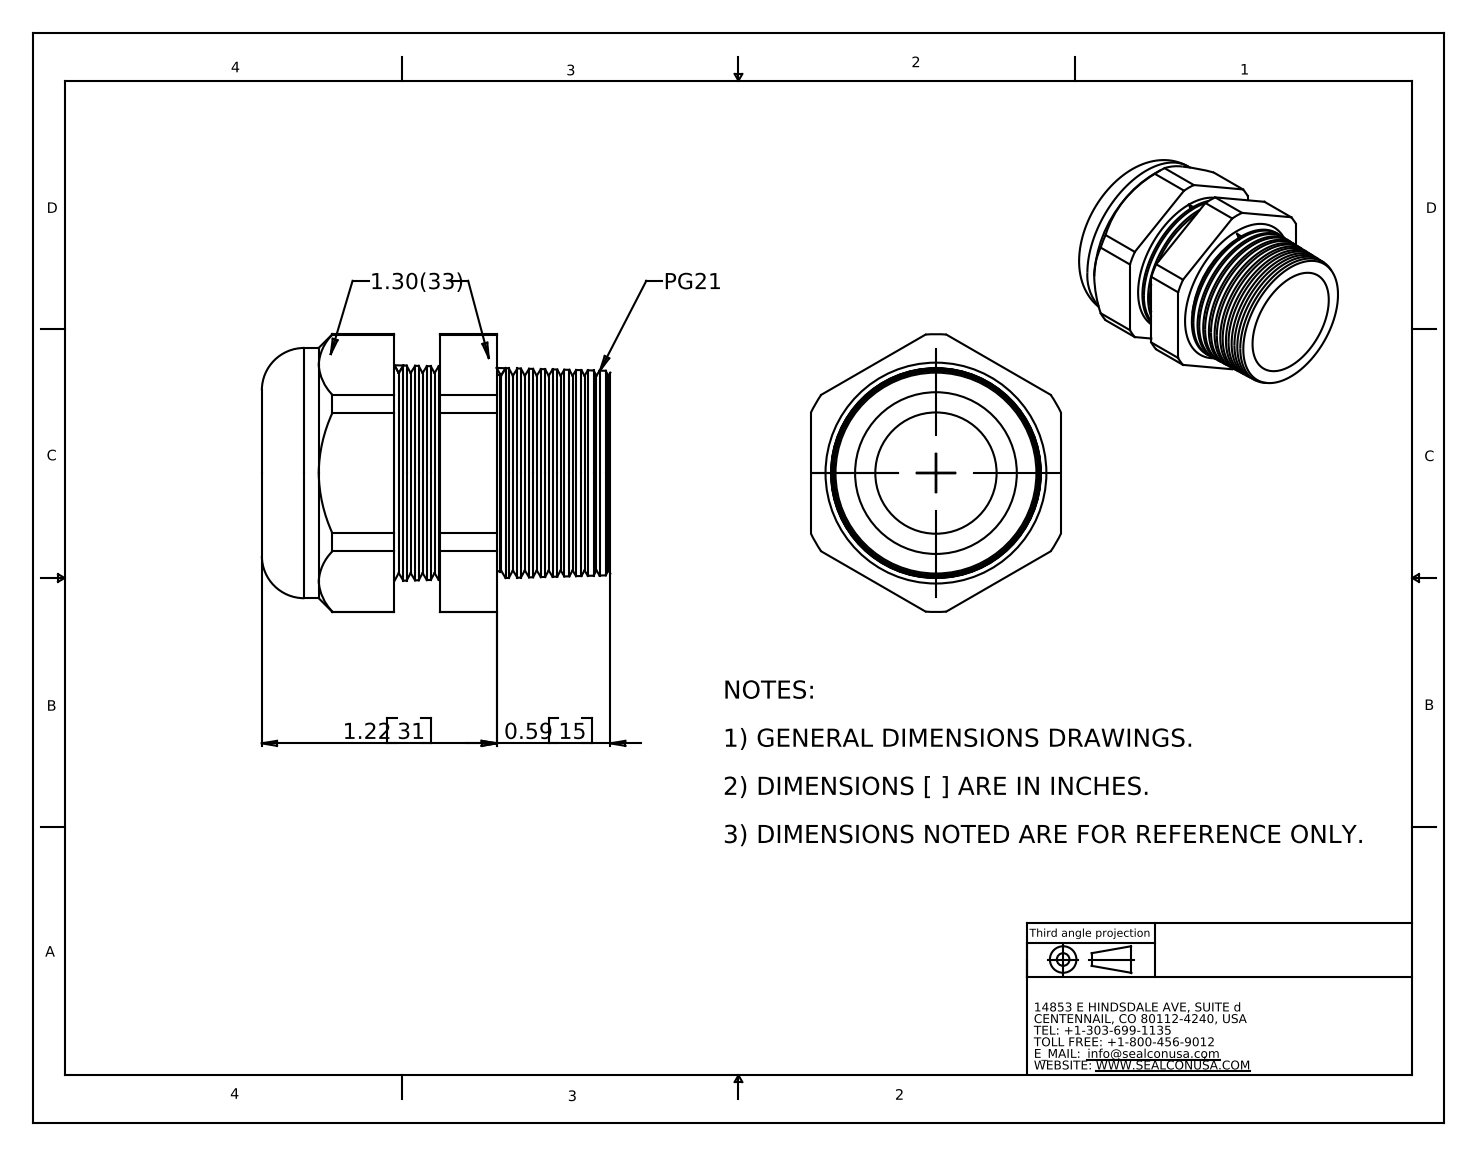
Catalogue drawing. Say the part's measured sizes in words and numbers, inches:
The part is named "CD21CR-GY". Its 3-D file was written by "SolidWorks 2007 (CONFIG_CONTROL_DESIGN)". It is 2 solids with 140 faces: 20 planar, 22 cylindrical and 98 other. Overall it measures 1.81 by 1.443 by 1.3 inches. Its volume is 1.379 cubic inches and its surface area 17.28 square inches. Round holes: 1 of diameter 0.63, 1 of diameter 0.84. Round bosses or shafts: 1 of diameter 1.3. Partial cylindrical surfaces (rounded edges, fillets, slot ends): 1 of radius 0.721. The main face-to-face distances are 1.3, 0.63, 0.394, 0.236, 0.295, 0.925, 0.531, 1.515, 1.121, 0.885.
